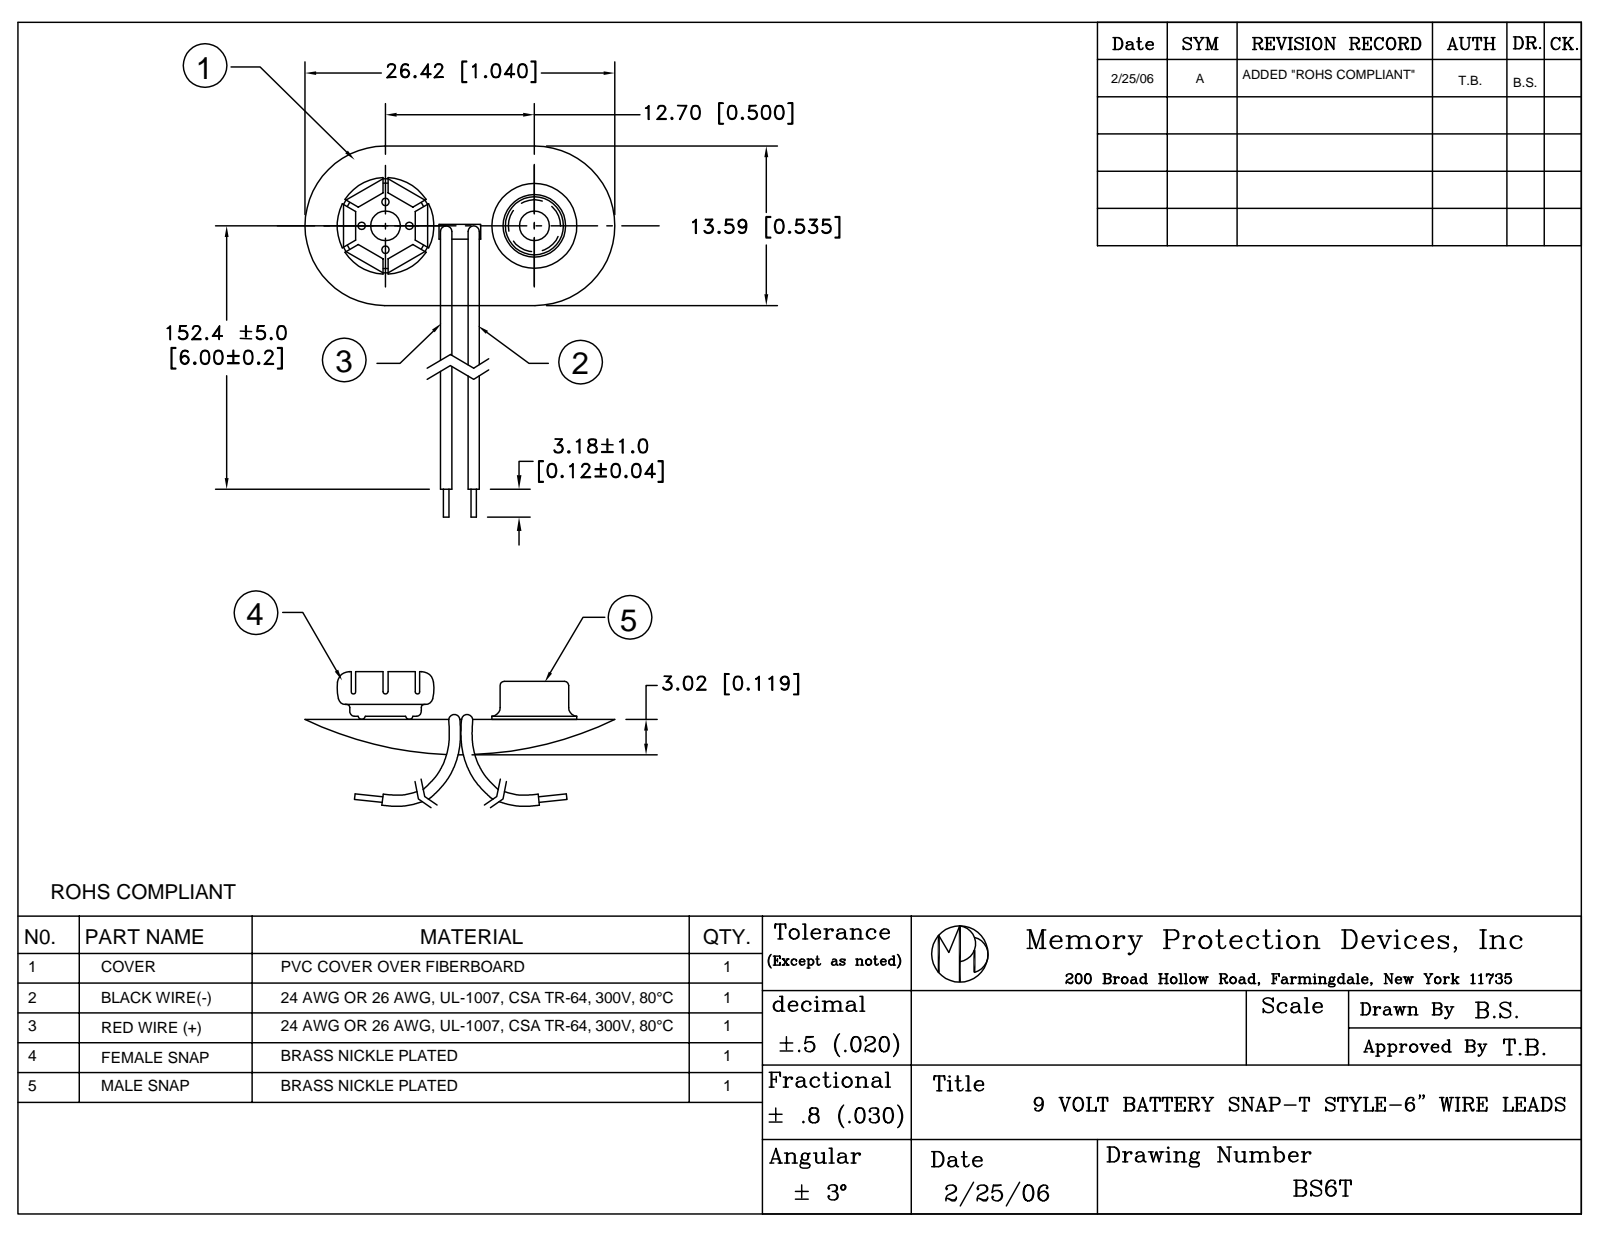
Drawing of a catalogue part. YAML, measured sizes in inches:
part_name: "BS6T"
step_written_by: "SolidWorks 2017 (AUTOMOTIVE_DESIGN)"
units: inches
bodies: {solids: 7, faces: 142, planar: 71, cylindrical: 47, other: 24}
overall_size: [6.24, 1.063, 0.333]
volume: 0.098
surface_area: 5.702
round_holes:
  - {diameter: 0.024, count: 4}
  - {diameter: 0.098, count: 2}
  - {diameter: 0.175, count: 1}
  - {diameter: 0.284, count: 1}
round_bosses_or_shafts:
  - {diameter: 0.055, count: 4}
  - {diameter: 0.023, count: 2}
  - {diameter: 0.315, count: 1}
  - {diameter: 0.276, count: 1}
  - {diameter: 0.236, count: 1}
  - {diameter: 0.205, count: 1}
partial_cylinders:
  - {radius: 0.01, count: 6}
  - {radius: 0.256, count: 2}
  - {radius: 0.886, count: 1}
face_to_face_distances: [0.512, 0.059, 0.047, 0.035, 0.024, 0.071, 0.083, 0.23, 0.094, 0.162]
hole_center_spacings: [0.083, 0.117, 0.165, 0.515, 0.425, 0.508, 0.591]
